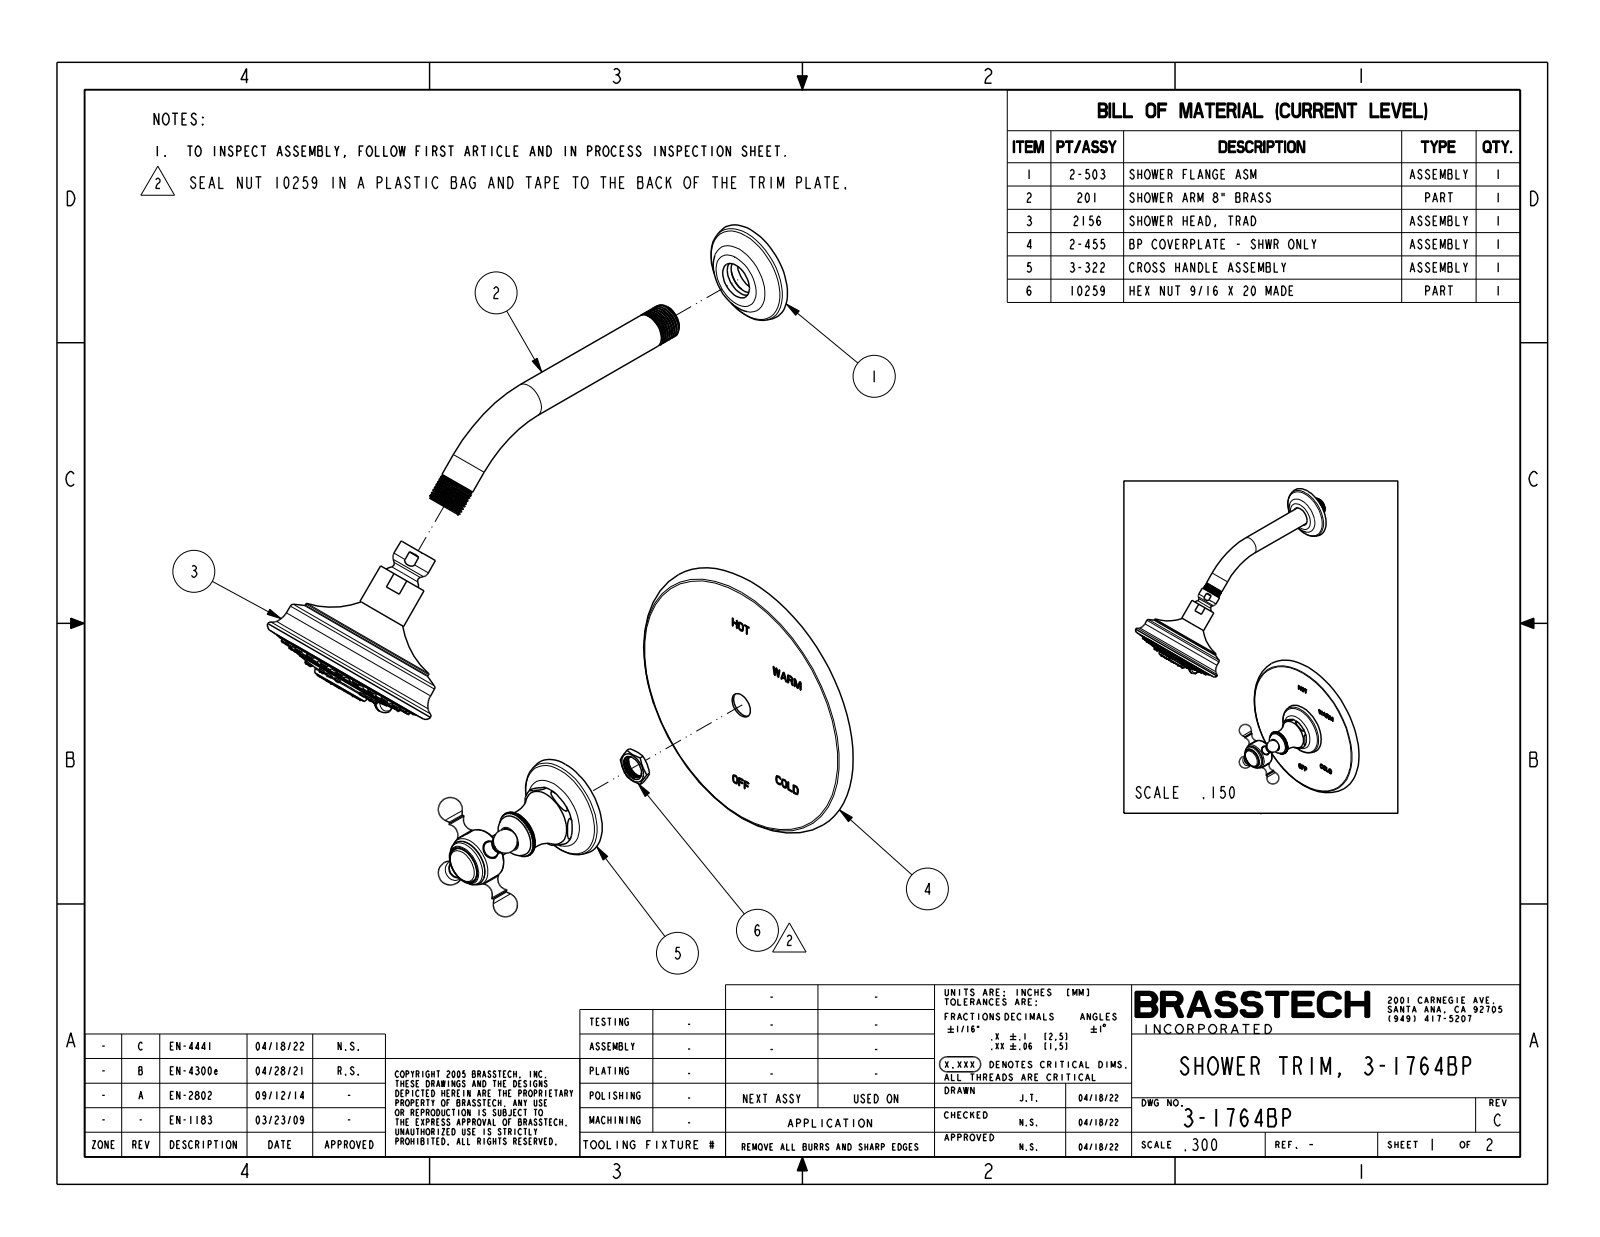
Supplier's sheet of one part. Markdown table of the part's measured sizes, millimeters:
| quantity | value |
| --- | --- |
| part name | 3-1764BP |
| STEP written by | CREO PARAMETRIC BY PTC INC, 2018400 (CONFIG_CONTROL_DESIGN) |
| units | millimeters |
| bodies | 2 solids, 1651 faces (618 planar, 212 cylindrical, 821 other) |
| overall size | 419 × 255.3 × 168.3 |
| volume | 578 000 mm³ |
| surface area | 109 000 mm² |
| round holes (diameter × count) | 1.5 × 8, 10.4 × 2, 21.7 × 1, 23.5 × 1 |
| round bosses / shafts (diameter × count) | 3.6 × 39, 4.2 × 23, 20.7 × 2, 10 × 2, 96.8 × 1, 94.6 × 1, 82.3 × 1, 59 × 1 |
| partial cylindrical surfaces (radius × count) | 2 × 8, 0.5 × 2, 3.5 × 1, 12 × 1, 13 × 1, 16 × 1 |
| main face-to-face distances | 8, 12.2, 4.2, 1.6, 3, 4.6, 72.5, 64.5, 60.3, 73.2 |
| hole center spacings | 14.7, 11.3, 27.2, 20.8, 20.8, 29.4, 11.3, 27.2 |
